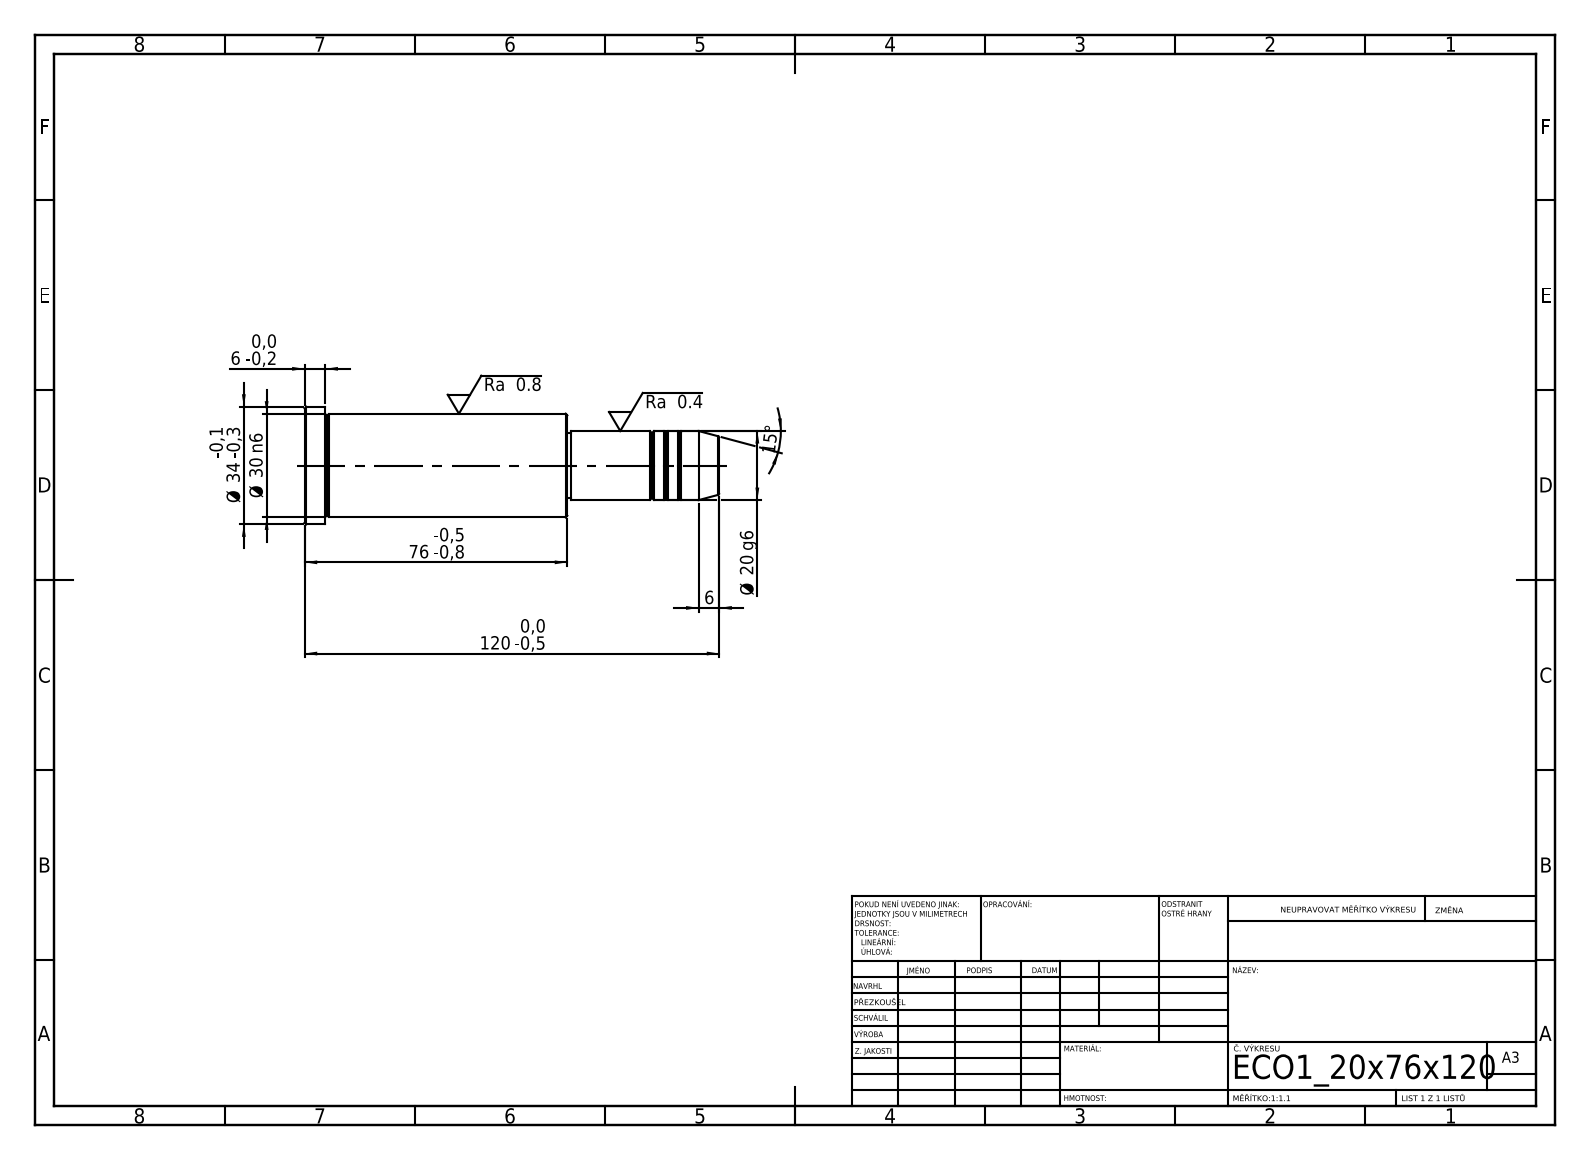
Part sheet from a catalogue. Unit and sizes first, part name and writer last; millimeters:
Units: millimetres
Overall size (bounding box): 120 × 34 × 34
Round bosses / shafts (diameter × count): ⌀34 ×1, ⌀30 ×1, ⌀20 ×1, ⌀19 ×1
Main face-to-face distances: 76, 44, 120, 114, 70, 6, 43, 1, 71, 77
Volume: 68 298 mm³ · Surface area: 11 849 mm²
Bodies: 1 solid, 43 faces (5 planar, 14 cylindrical, 24 other)
STEP written by: SolidWorks 2019 (CONFIG_CONTROL_DESIGN)
